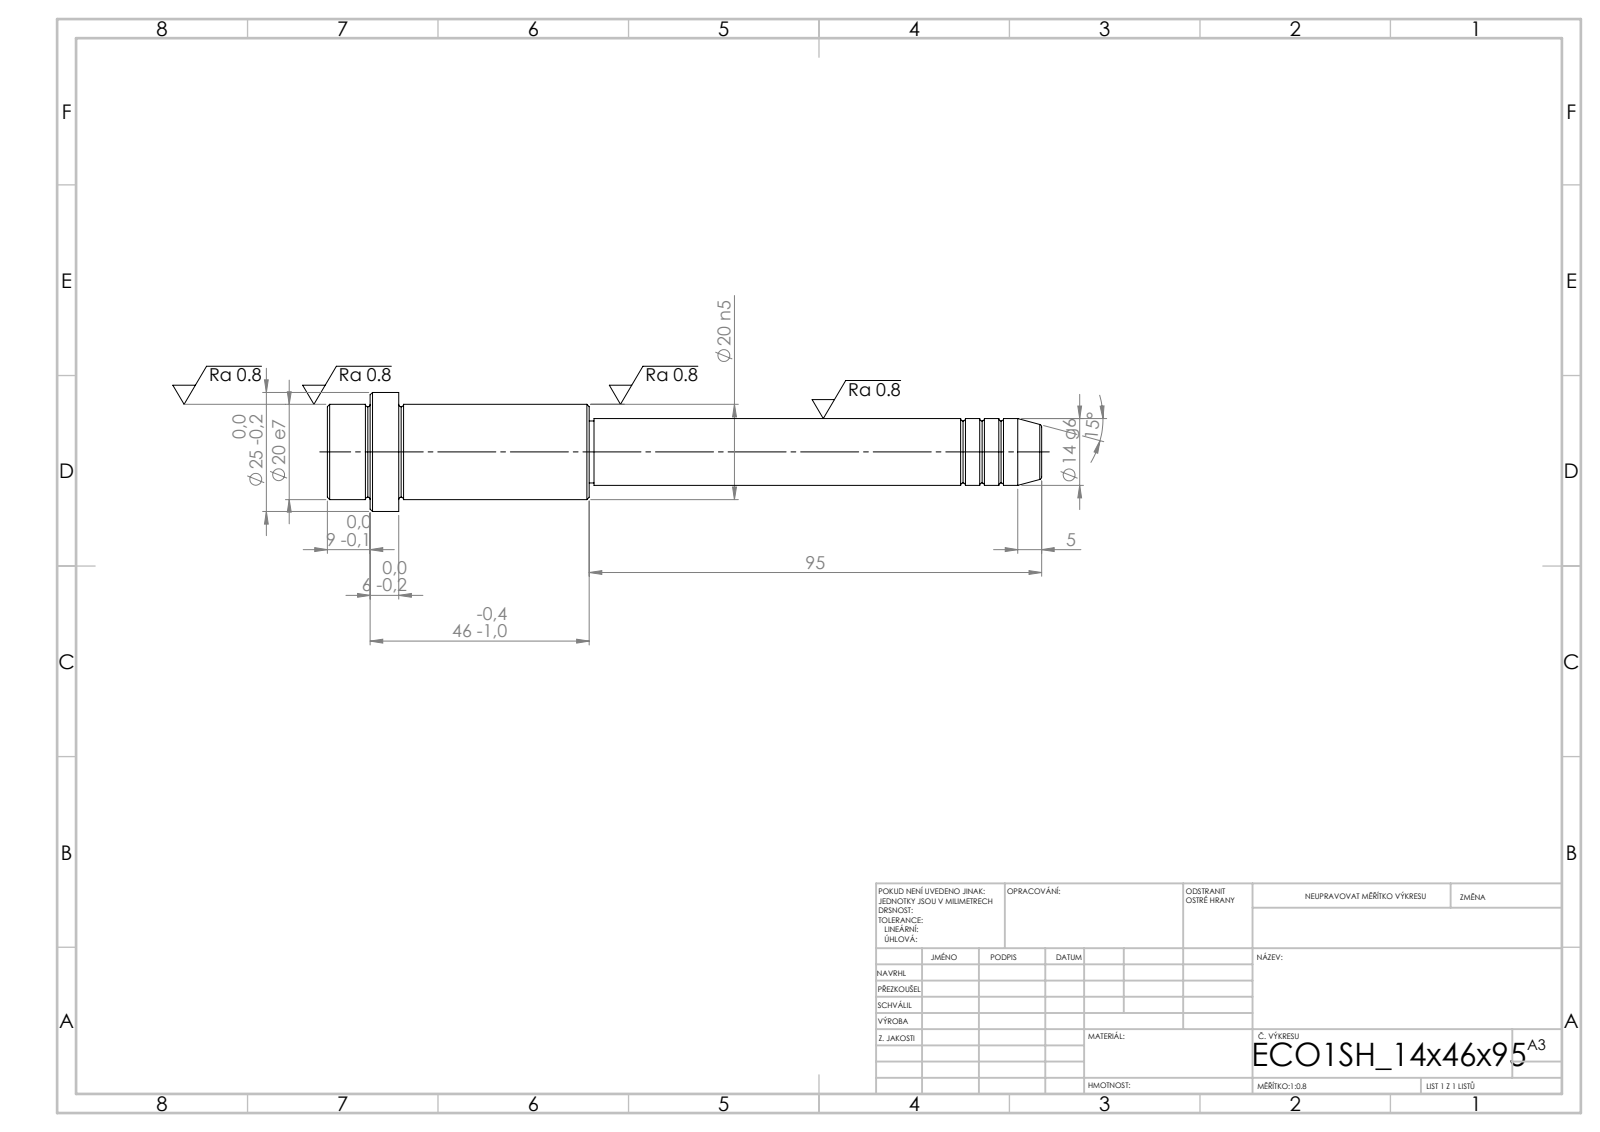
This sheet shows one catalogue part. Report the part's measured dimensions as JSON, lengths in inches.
{"step_written_by": "SolidWorks 2019 (CONFIG_CONTROL_DESIGN)", "units": "inches", "bodies": {"solids": 1, "faces": 52, "planar": 6, "cylindrical": 16, "other": 30}, "overall_size": [5.906, 0.984, 0.984], "volume_in3": 1.994, "surface_area_in2": 13.56, "round_bosses_or_shafts": [[0.984, 1], [0.787, 1], [0.551, 1], [0.512, 1]], "face_to_face_distances": [0.591, 1.575, 2.165, 1.811, 0.236, 0.354, 3.74, 5.315, 5.551, 5.906]}
